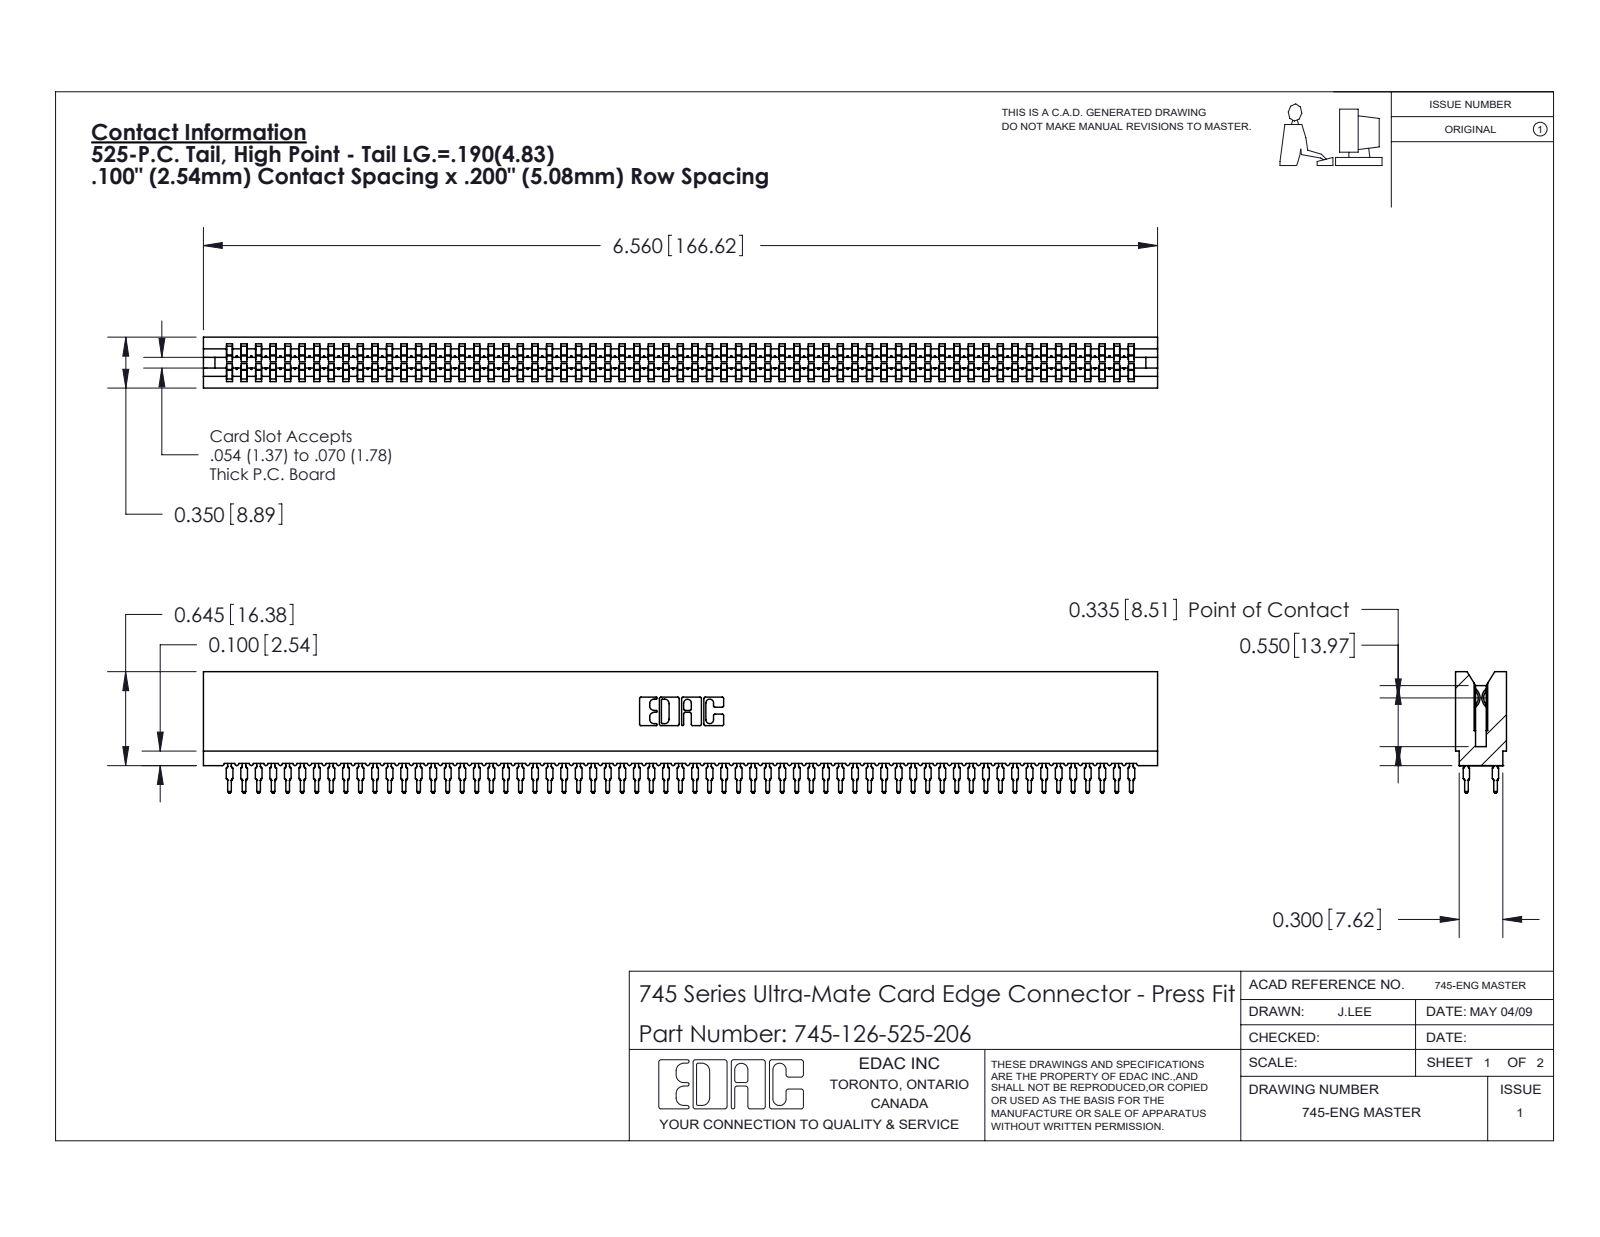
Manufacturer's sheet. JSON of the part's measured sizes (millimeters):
{"part_name": "745 Part_Insulator Option - 06; 745-126-525-206; 745-292-001_525", "step_written_by": "SolidWorks 2020 (CONFIG_CONTROL_DESIGN)", "units": "millimeters", "bodies": {"solids": 127, "faces": 11373, "planar": 5852, "cylindrical": 2245, "other": 3276}, "overall_size": [166.6, 21.2, 8.9], "volume_mm3": 14800, "surface_area_mm2": 30530, "partial_cylinders_radius": [[0.5, 252], [0.4, 126], [0.3, 22], [0.1, 8], [0.3, 8], [0.2, 6], [0.8, 6], [0.7, 3]], "face_to_face_distances": [8.9, 1.6, 7.3, 1.1, 7.7, 0.5, 6.2, 3.5, 5.4, 2.4]}
